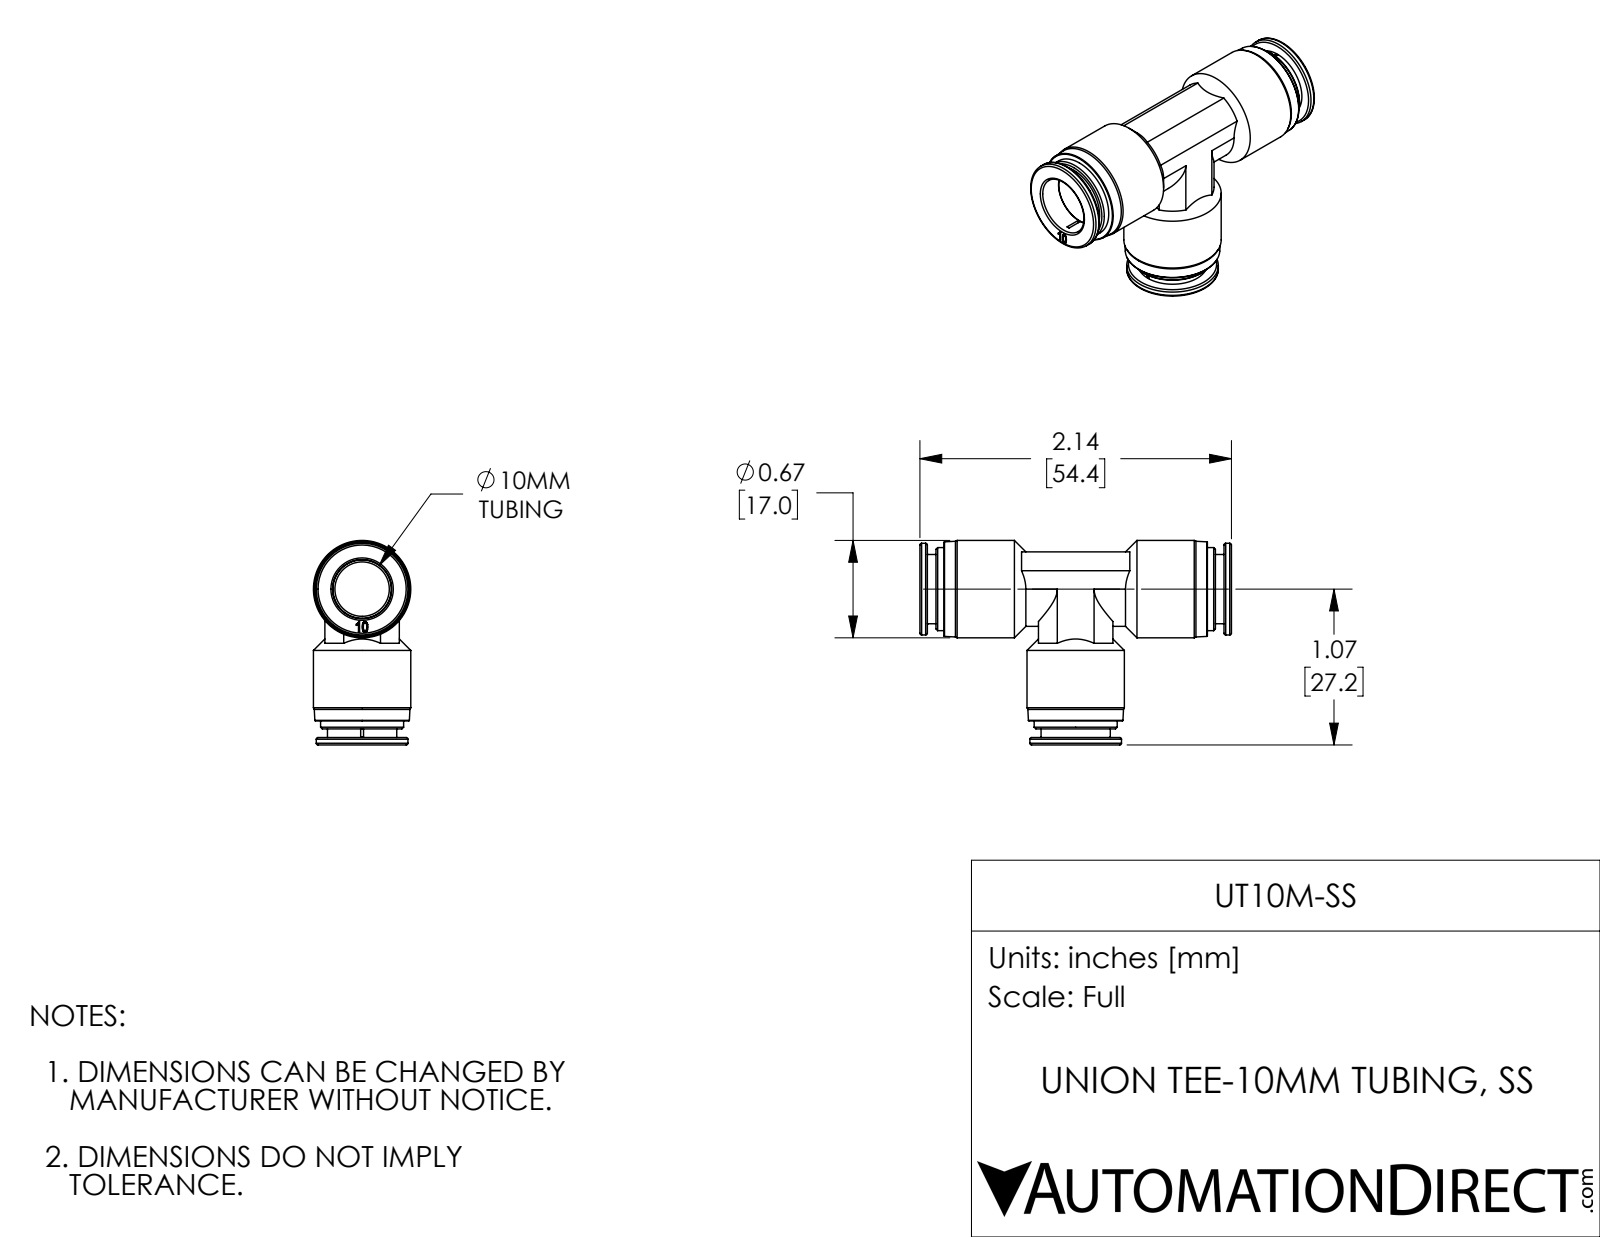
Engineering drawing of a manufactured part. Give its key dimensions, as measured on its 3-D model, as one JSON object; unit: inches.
{"part_name": "UT10M-SS", "step_written_by": "SolidWorks 2017 (AUTOMOTIVE_DESIGN)", "units": "inches", "bodies": {"solids": 1, "faces": 213, "planar": 65, "cylindrical": 49, "other": 99}, "overall_size": [2.142, 1.406, 0.669], "volume_in3": 0.496, "surface_area_in2": 11.26, "round_holes": [[0.374, 2], [0.402, 2], [0.406, 2]], "round_bosses_or_shafts": [[0.669, 2], [0.63, 2], [0.571, 2], [0.476, 2]], "partial_cylinders_radius": [[0.256, 1]], "face_to_face_distances": [0.051, 0.114, 0.165, 2.091, 0.512, 1.327, 1.276, 1.976, 1.925, 2.142]}
